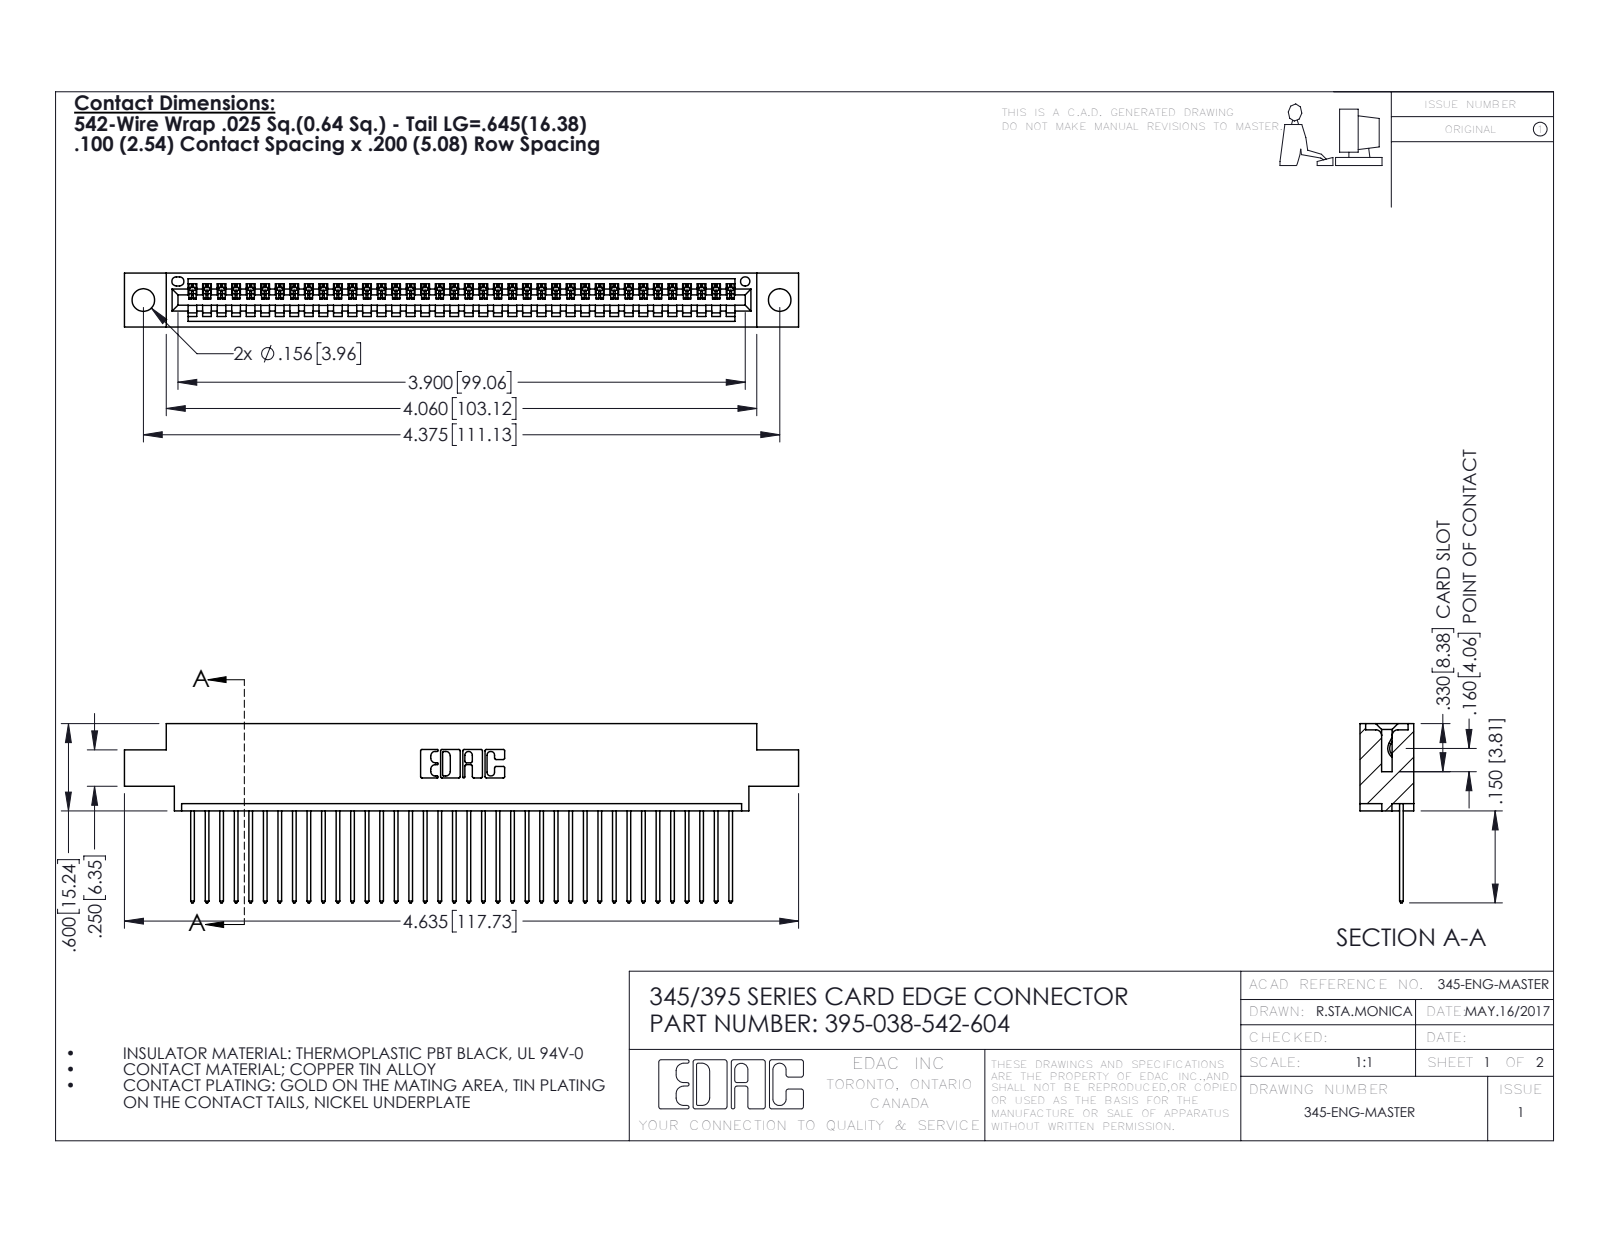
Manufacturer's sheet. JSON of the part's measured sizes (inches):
{"part_name": "345-292-001_345-293-142; 395-038-542-604; 345 Part_0.170 Offset - 0.156 Dia-TH", "step_written_by": "SolidWorks 2016 (CONFIG_CONTROL_DESIGN)", "units": "inches", "bodies": {"solids": 39, "faces": 2334, "planar": 1604, "cylindrical": 730, "other": 0}, "overall_size": [4.635, 1.232, 0.37], "volume_in3": 0.673, "surface_area_in2": 23.37, "round_holes": [[0.156, 2], [0.064, 1]], "partial_cylinders_radius": [[0.006, 76], [0.01, 76], [0.01, 22], [0.007, 6], [0.031, 6], [0.026, 3], [0.031, 2], [0.04, 2]], "face_to_face_distances": [0.072, 0.298, 0.37, 0.098, 0.272, 0.025, 0.2, 0.225, 0.175, 0.149], "hole_center_spacings": [0.27, 4.139, 4.375]}
